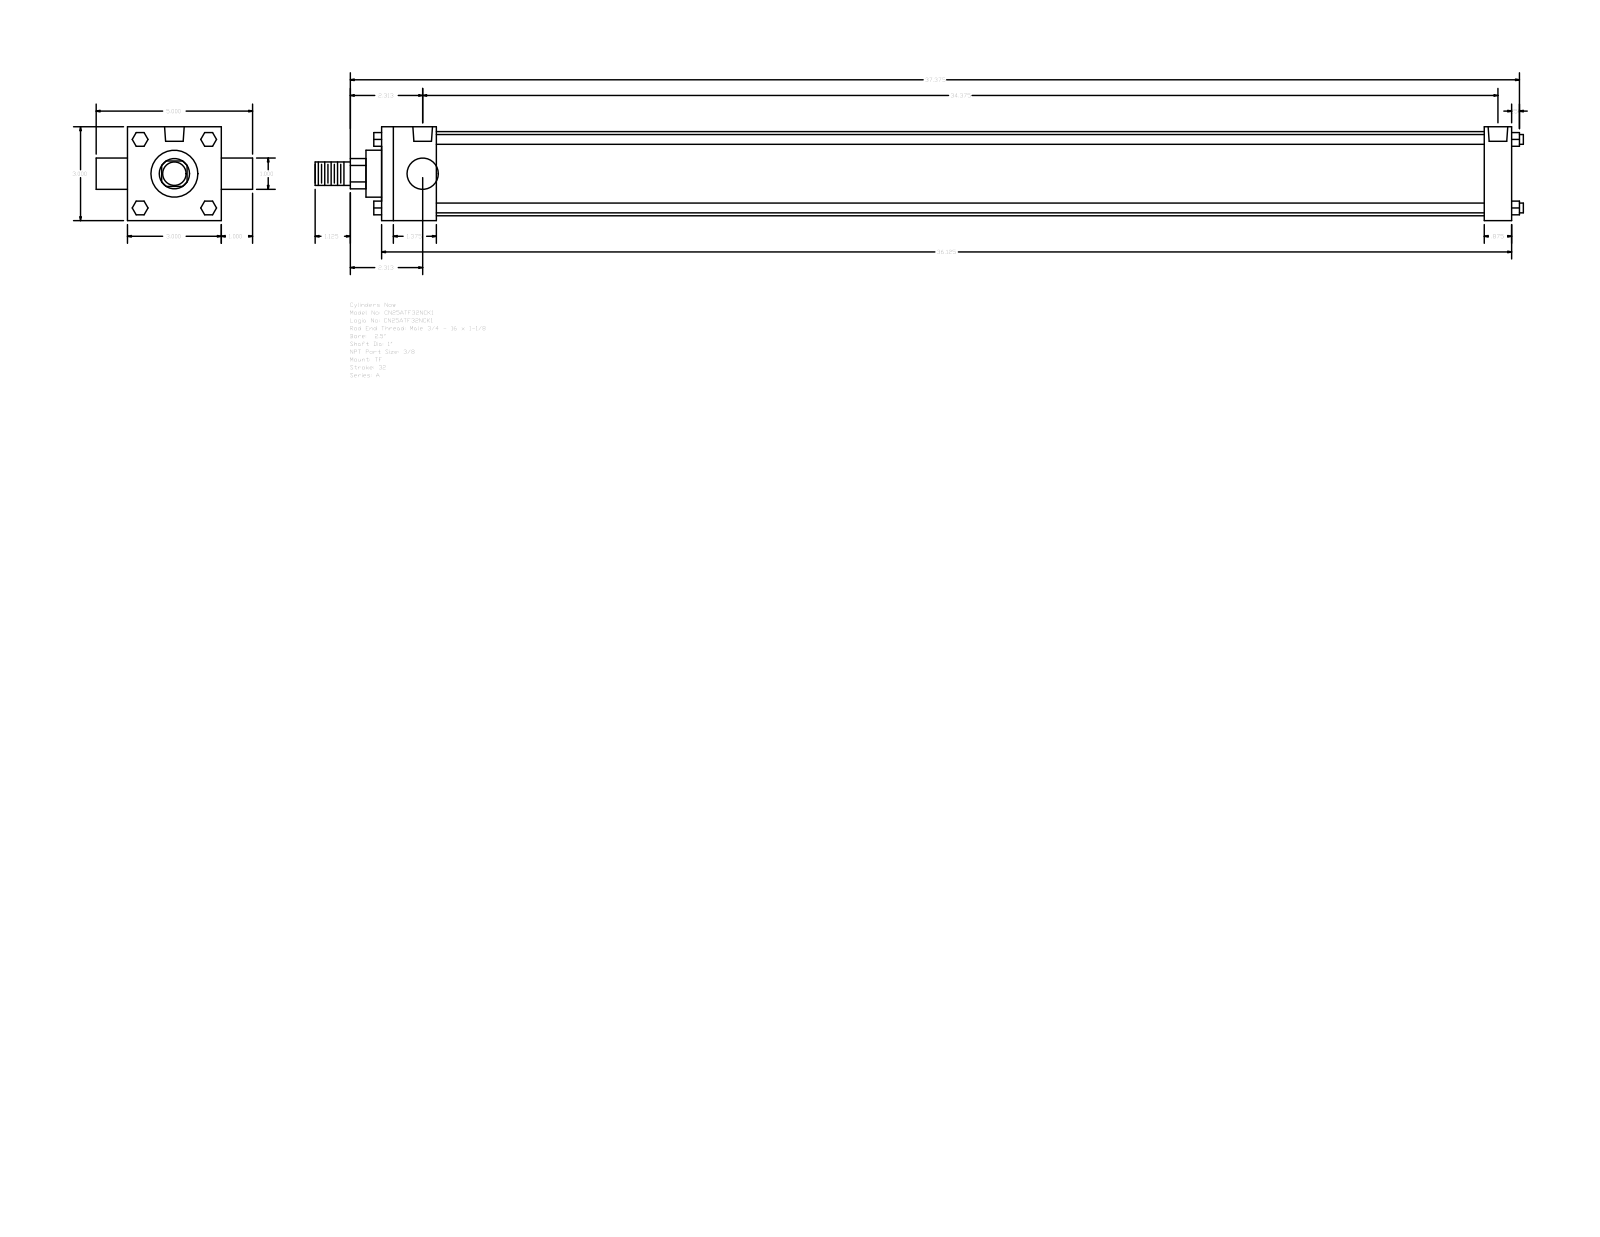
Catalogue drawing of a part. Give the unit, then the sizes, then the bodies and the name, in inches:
Units: inches
Overall size (bounding box): 38.625 × 5 × 3
Round holes (diameter × count): ⌀0.219 ×3, ⌀0.627 ×2
Round bosses / shafts (diameter × count): ⌀0.313 ×4, ⌀1 ×2, ⌀2.69 ×1, ⌀1.5 ×1, ⌀0.75 ×1
Partial cylindrical surfaces — rounded edges, fillets, slot ends (radius × count): R0.484 ×1
Main face-to-face distances: 3, 36.125, 1.75, 35.25, 33.5, 34.375, 0.875, 1, 4, 36.625
Hole centre spacings: 0.094, 34.469, 34.375, 34.562
Bodies: 0 solids, 120 faces (92 planar, 28 cylindrical, 0 other)
Part name (STEP PRODUCT): A_TF__0250_1
STEP written by: GSSL Pune (CONFIG_CONTROL_DESIGN)
